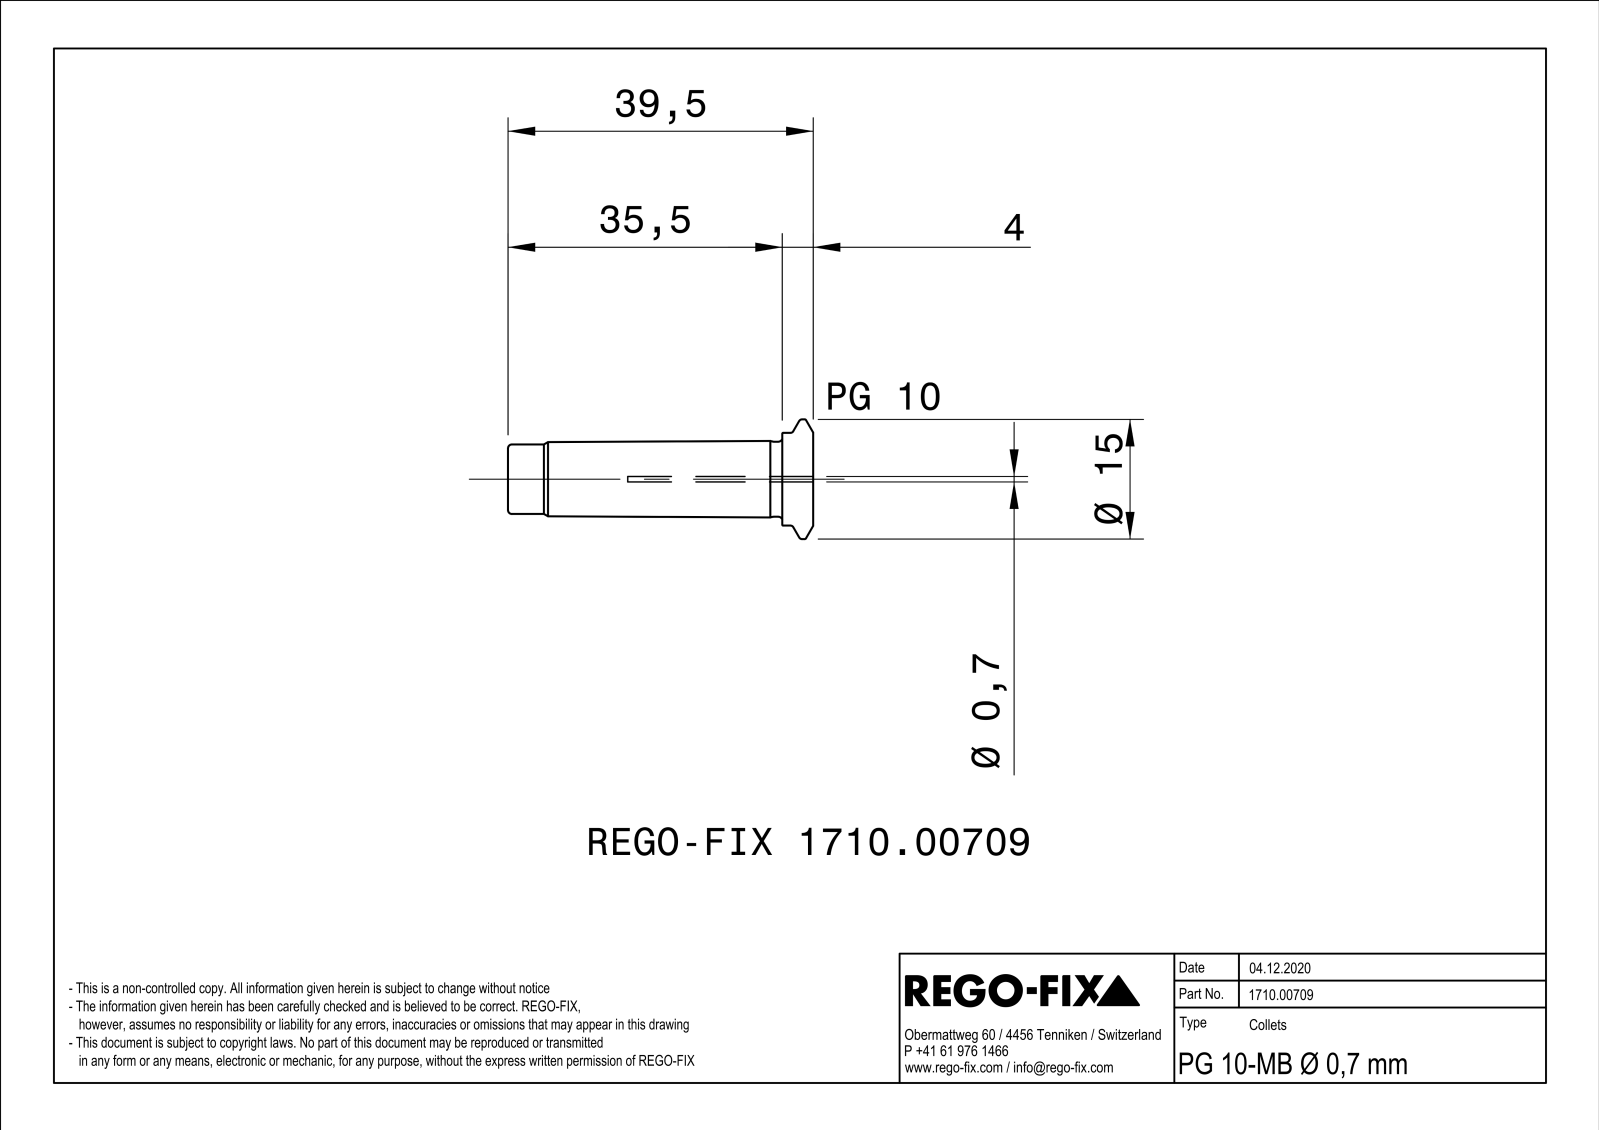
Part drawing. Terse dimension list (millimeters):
name: NOCUT
written by: SIEMENS PLM Software Solid Edge ST10 (AUTOMOTIVE_DESIGN)
unit: mm
bodies: 1 solid, 79 faces (21 planar, 18 cylindrical, 40 other)
size: 39.5 × 15.5 × 15.49
volume: 2 269 mm³; area: 2 679 mm²
holes: 3× ⌀2, 1× ⌀0.7, 1× ⌀6.19, 1× ⌀6.8
bosses: 1× ⌀15.5, 1× ⌀12, 1× ⌀9.7, 1× ⌀9
face distances: 0.6, 39.5, 19.5, 20, 35.5, 16, 4
hole spacings: 2, 3.46
